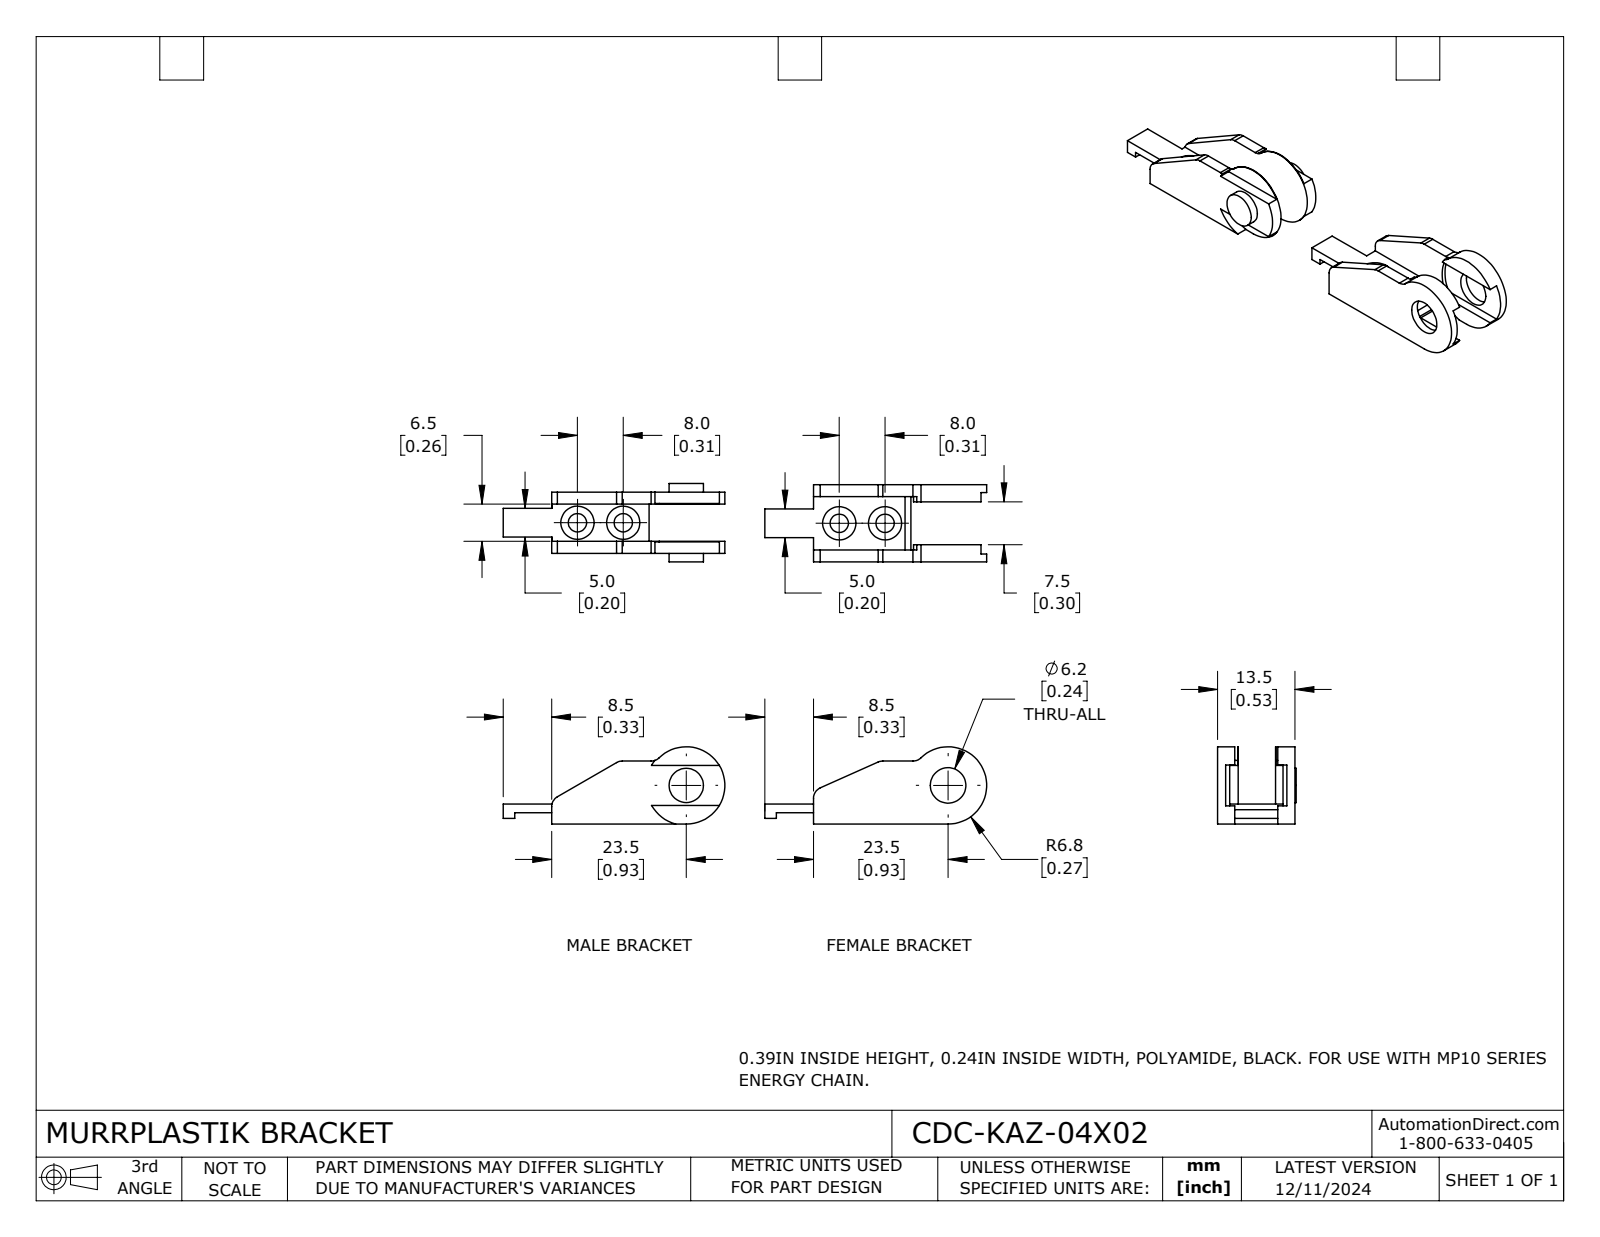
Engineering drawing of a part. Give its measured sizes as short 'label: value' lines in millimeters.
name: CDC-KAZ-04X02
written by: SolidWorks 2024 (AUTOMOTIVE_DESIGN)
unit: mm
bodies: 2 solids, 96 faces (56 planar, 36 cylindrical, 4 other)
size: 84.4 × 13.7 × 13.5
volume: 3 210 mm³; area: 3 916 mm²
holes: 4× ⌀3.2, 1× ⌀6.2
bosses: 1× ⌀6
rounds: 6× R2, 2× R1, 2× R6.8, 2× R7
face distances: 2.1, 8.6, 1.5, 10.1, 9.9, 3.5, 1.3, 10.7, 13.5, 3.6
hole spacings: 8, 45.7, 37.7, 53.7
